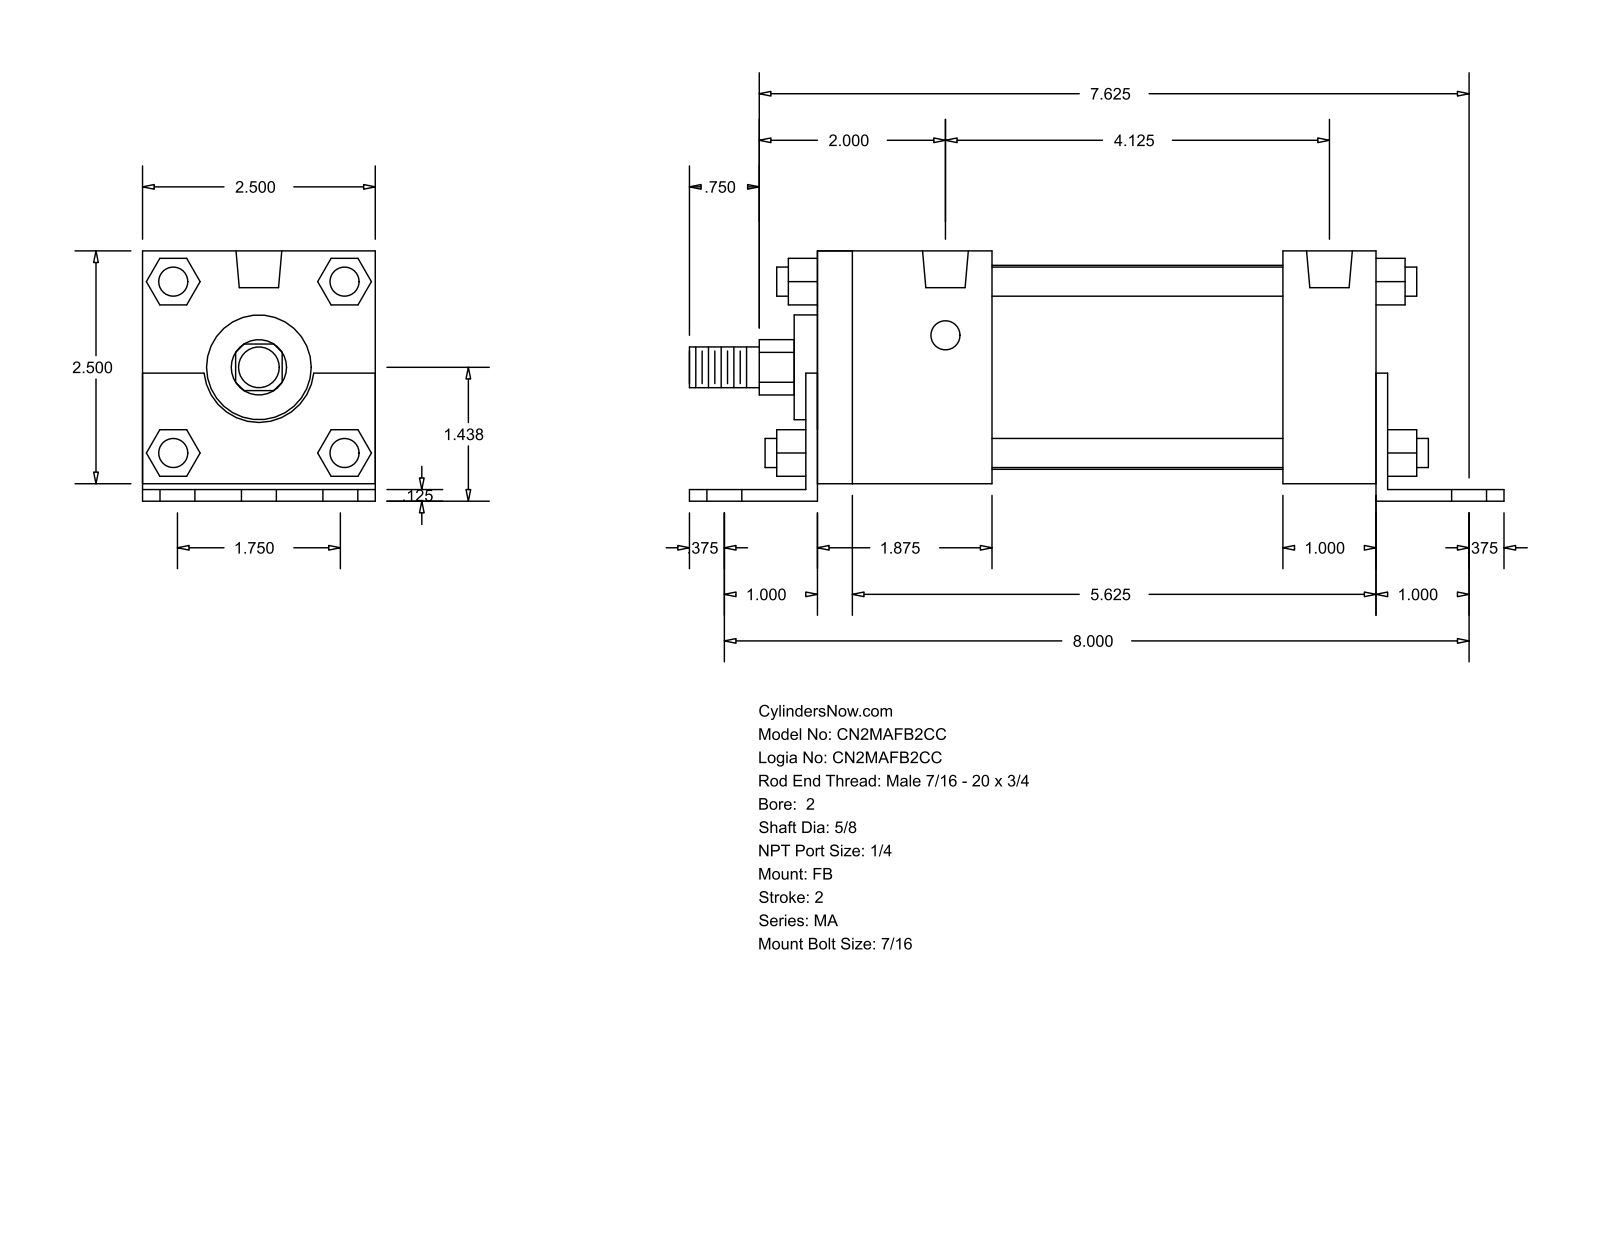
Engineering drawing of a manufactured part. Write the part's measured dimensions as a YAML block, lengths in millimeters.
part_name: "MA_FB__0200_0.625"
step_written_by: "GSSL Pune (CONFIG_CONTROL_DESIGN)"
units: millimeters
bodies: {solids: 0, faces: 140, planar: 105, cylindrical: 35, other: 0}
overall_size: [222.25, 68.26, 63.5]
round_holes:
  - {diameter: 11.11, count: 6}
  - {diameter: 7.94, count: 4}
  - {diameter: 12.49, count: 2}
round_bosses_or_shafts:
  - {diameter: 7.94, count: 4}
  - {diameter: 55.63, count: 1}
  - {diameter: 28.57, count: 1}
  - {diameter: 15.88, count: 1}
  - {diameter: 11.11, count: 1}
partial_cylinders:
  - {radius: 7.54, count: 1}
  - {radius: 15.05, count: 1}
face_to_face_distances: [63.5, 3.17, 4.76, 68.26, 1.59, 65.09, 158.75, 3.18, 152.4, 155.57]
hole_center_spacings: [22.23, 204.42, 203.21, 44.12, 44.46, 64.3, 104.77, 144.6]
